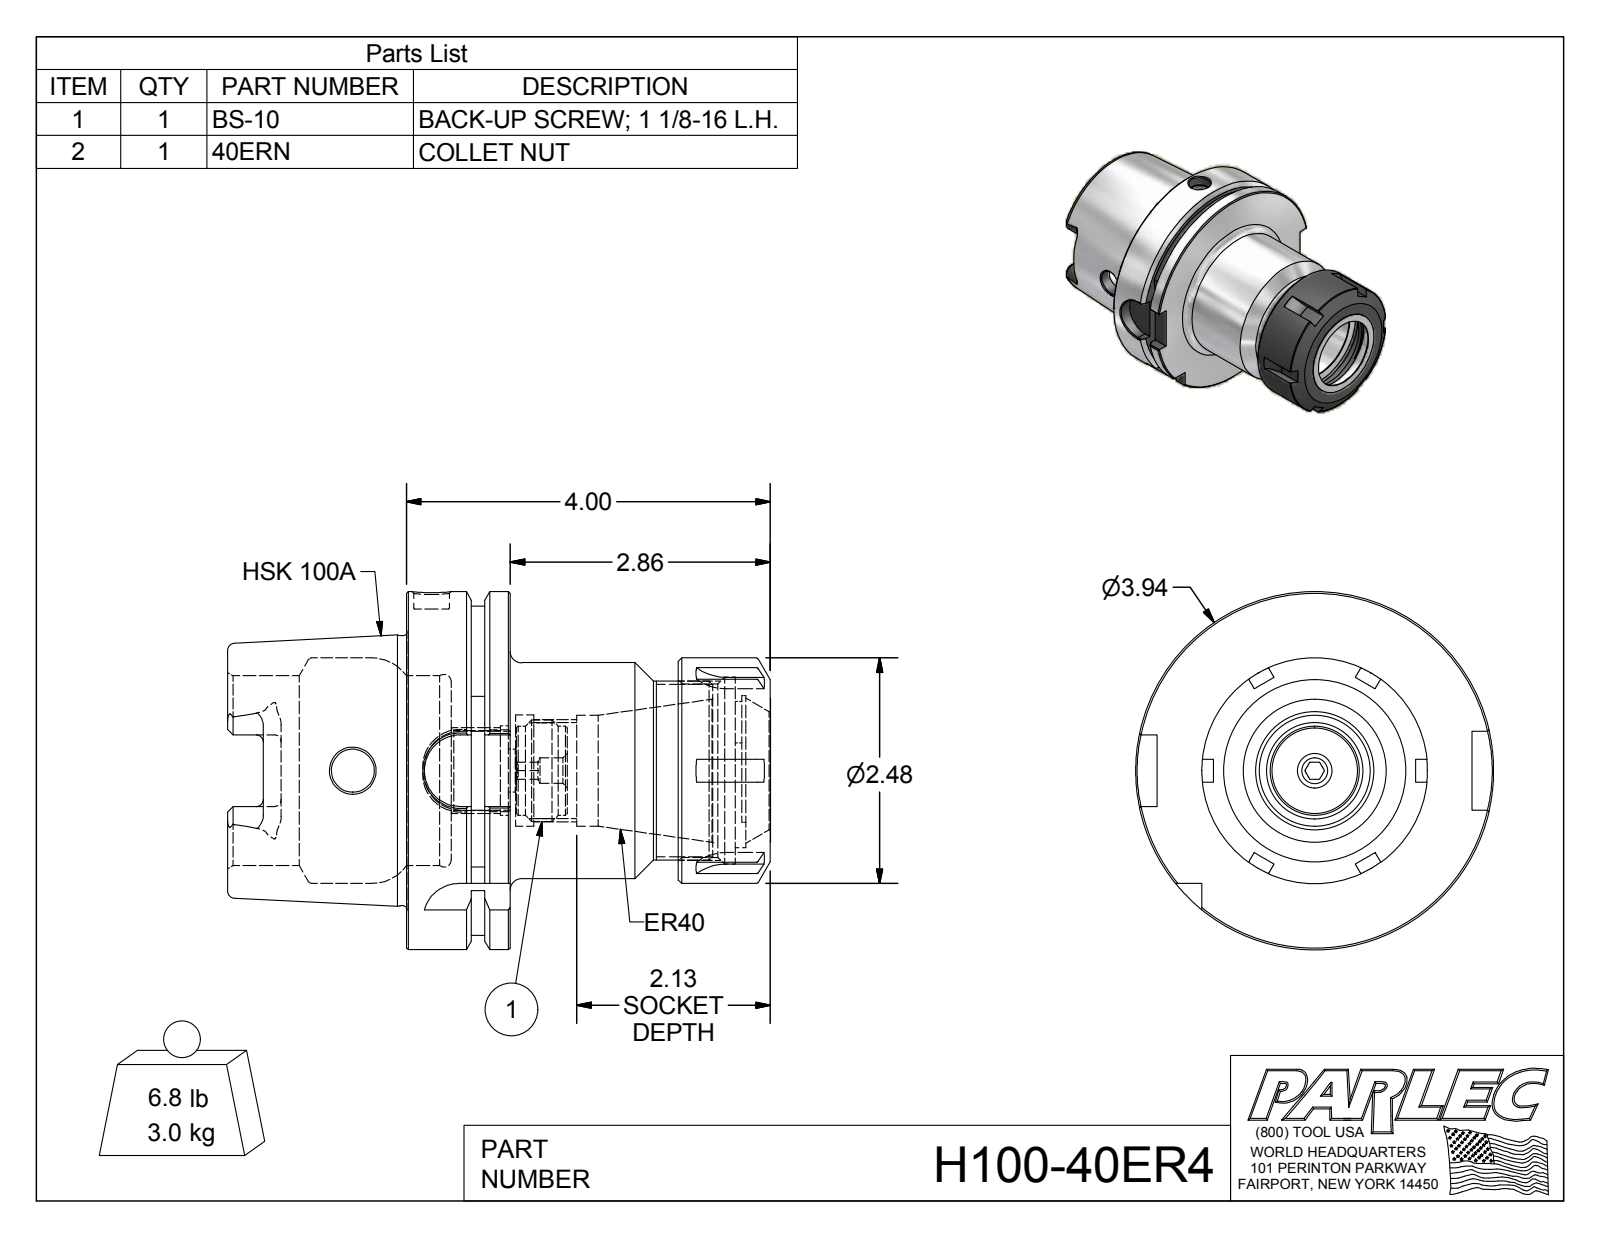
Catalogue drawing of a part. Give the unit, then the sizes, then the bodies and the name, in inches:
Units: inches
Overall size (bounding box): 5.974 × 3.937 × 3.937
Round holes (diameter × count): ⌀0.472 ×2, ⌀0.22 ×1, ⌀0.28 ×1, ⌀0.394 ×1, ⌀0.881 ×1, ⌀0.985 ×1, ⌀1.057 ×1, ⌀1.22 ×1, ⌀1.225 ×1, ⌀1.298 ×1, ⌀1.909 ×1, ⌀2.057 ×1
Round bosses / shafts (diameter × count): ⌀3.937 ×1, ⌀2.967 ×1, ⌀2.375 ×1, ⌀1.969 ×1, ⌀1.575 ×1, ⌀1.118 ×1, ⌀0.98 ×1
Partial cylindrical surfaces — rounded edges, fillets, slot ends (radius × count): R0.079 ×6, R0.501 ×6, R0.192 ×4, R0.394 ×4, R0.762 ×1, R0.787 ×1, R0.827 ×1, R1.811 ×1
Main face-to-face distances: 1.142, 0.63, 0.492, 0.65, 0.382, 2.496, 2.988, 1.846, 2.878, 1.969
Volume: 24 in³ · Surface area: 124.9 in²
Bodies: 3 solids, 200 faces (77 planar, 55 cylindrical, 68 other)
Part name (STEP PRODUCT): H100-40ER4; H100-40ER4-1; BS-10; 40ERN
STEP written by: Autodesk Inventor 2012 (AUTOMOTIVE_DESIGN)
